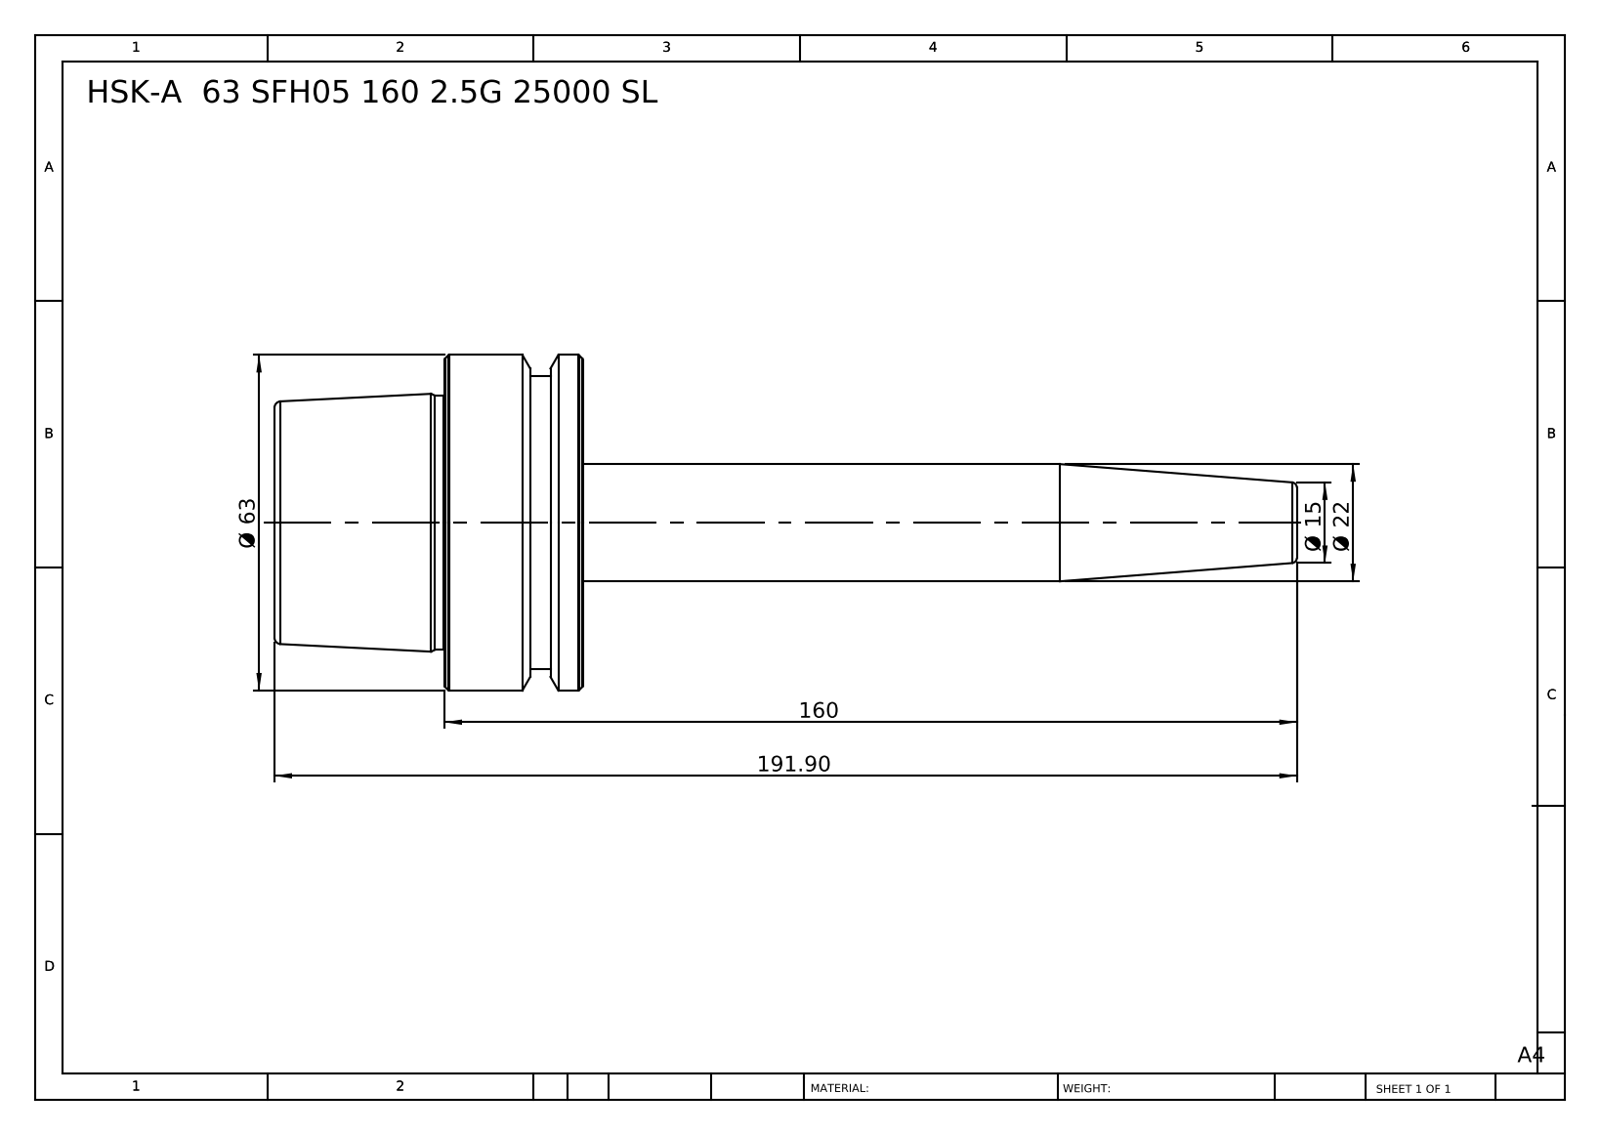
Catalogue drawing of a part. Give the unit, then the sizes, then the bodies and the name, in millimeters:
Units: millimetres
Overall size (bounding box): 191.9 × 63 × 63
Round bosses / shafts (diameter × count): ⌀63 ×1, ⌀55 ×1, ⌀47.78 ×1, ⌀22 ×1
Main face-to-face distances: 57.9, 26, 31.9, 6.1, 19.9, 51.8, 9.9, 3.8, 16.1, 48
Volume: 178 717 mm³ · Surface area: 25 209 mm²
Bodies: 1 solid, 46 faces (6 planar, 10 cylindrical, 30 other)
Part name (STEP PRODUCT): HSK-A 63 SFH04 160 2.5G 25000 SL
STEP written by: SolidWorks 2014 (CONFIG_CONTROL_DESIGN)
